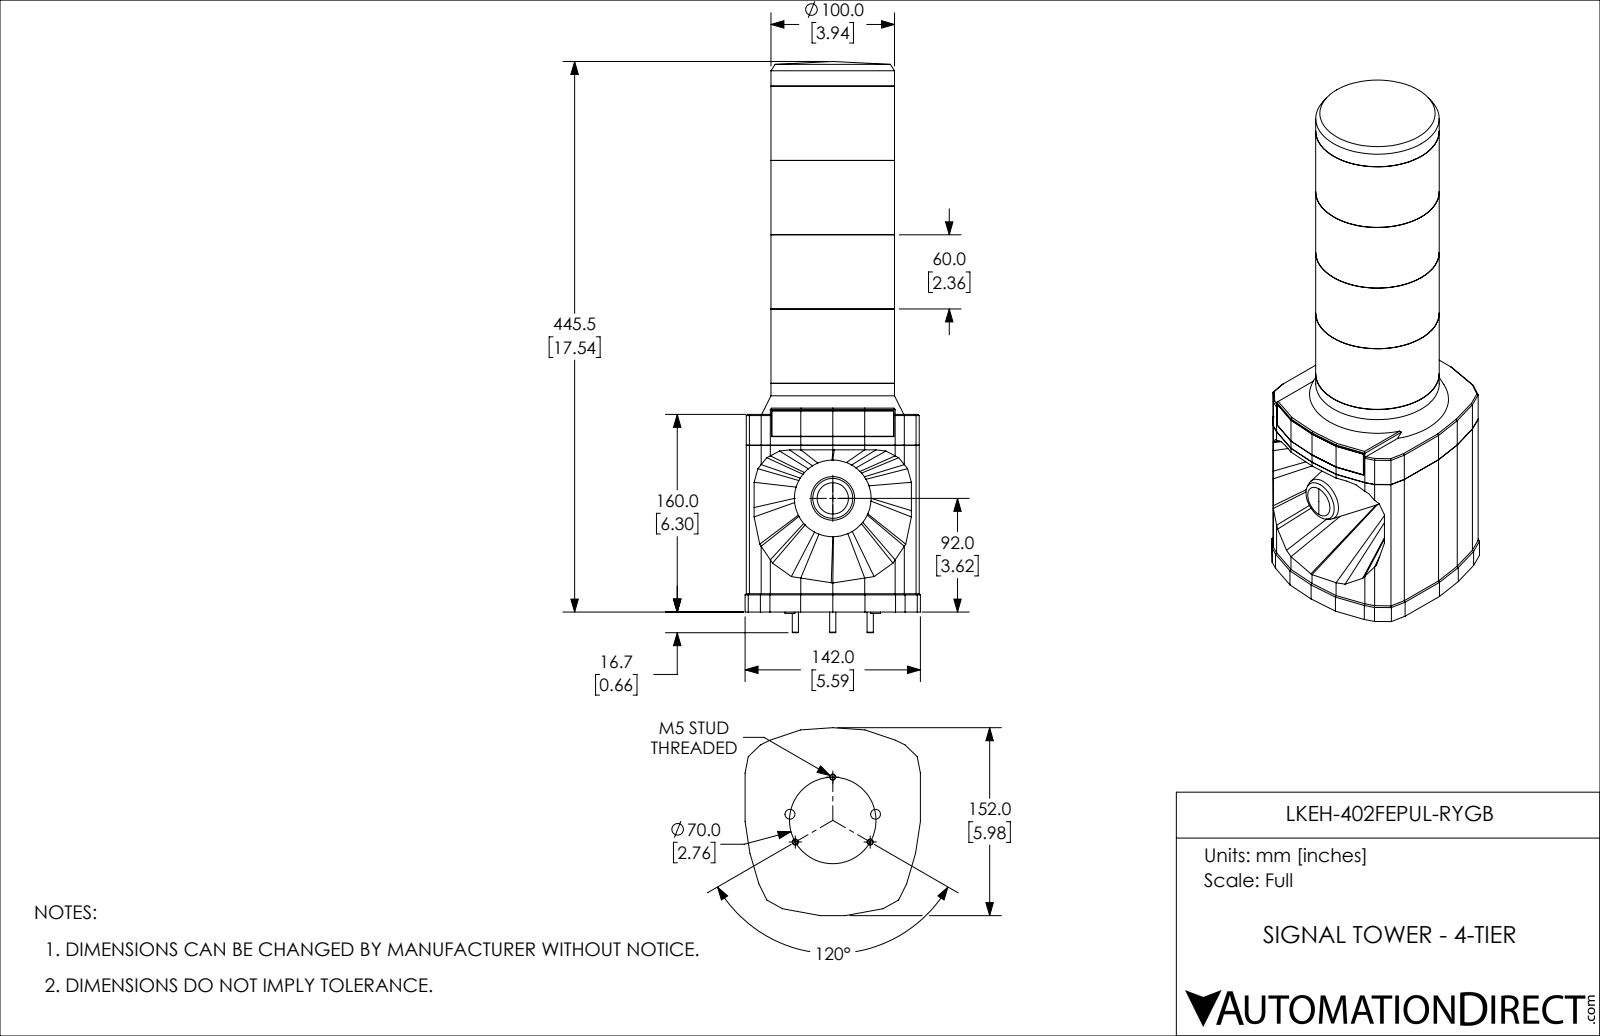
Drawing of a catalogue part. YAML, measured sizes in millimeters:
part_name: "LKEH-402FEPUL-RYGB"
step_written_by: "SolidWorks 2018 (AUTOMOTIVE_DESIGN)"
units: millimeters
bodies: {solids: 1, faces: 278, planar: 186, cylindrical: 32, other: 60}
overall_size: [462.2, 152, 142]
volume: 4742000
surface_area: 236500
round_bosses_or_shafts:
  - {diameter: 5, count: 3}
  - {diameter: 8, count: 2}
  - {diameter: 100, count: 1}
  - {diameter: 95.6, count: 1}
face_to_face_distances: [1, 140, 160, 60.1, 120.2, 60.2, 60, 165, 5, 180.3]
